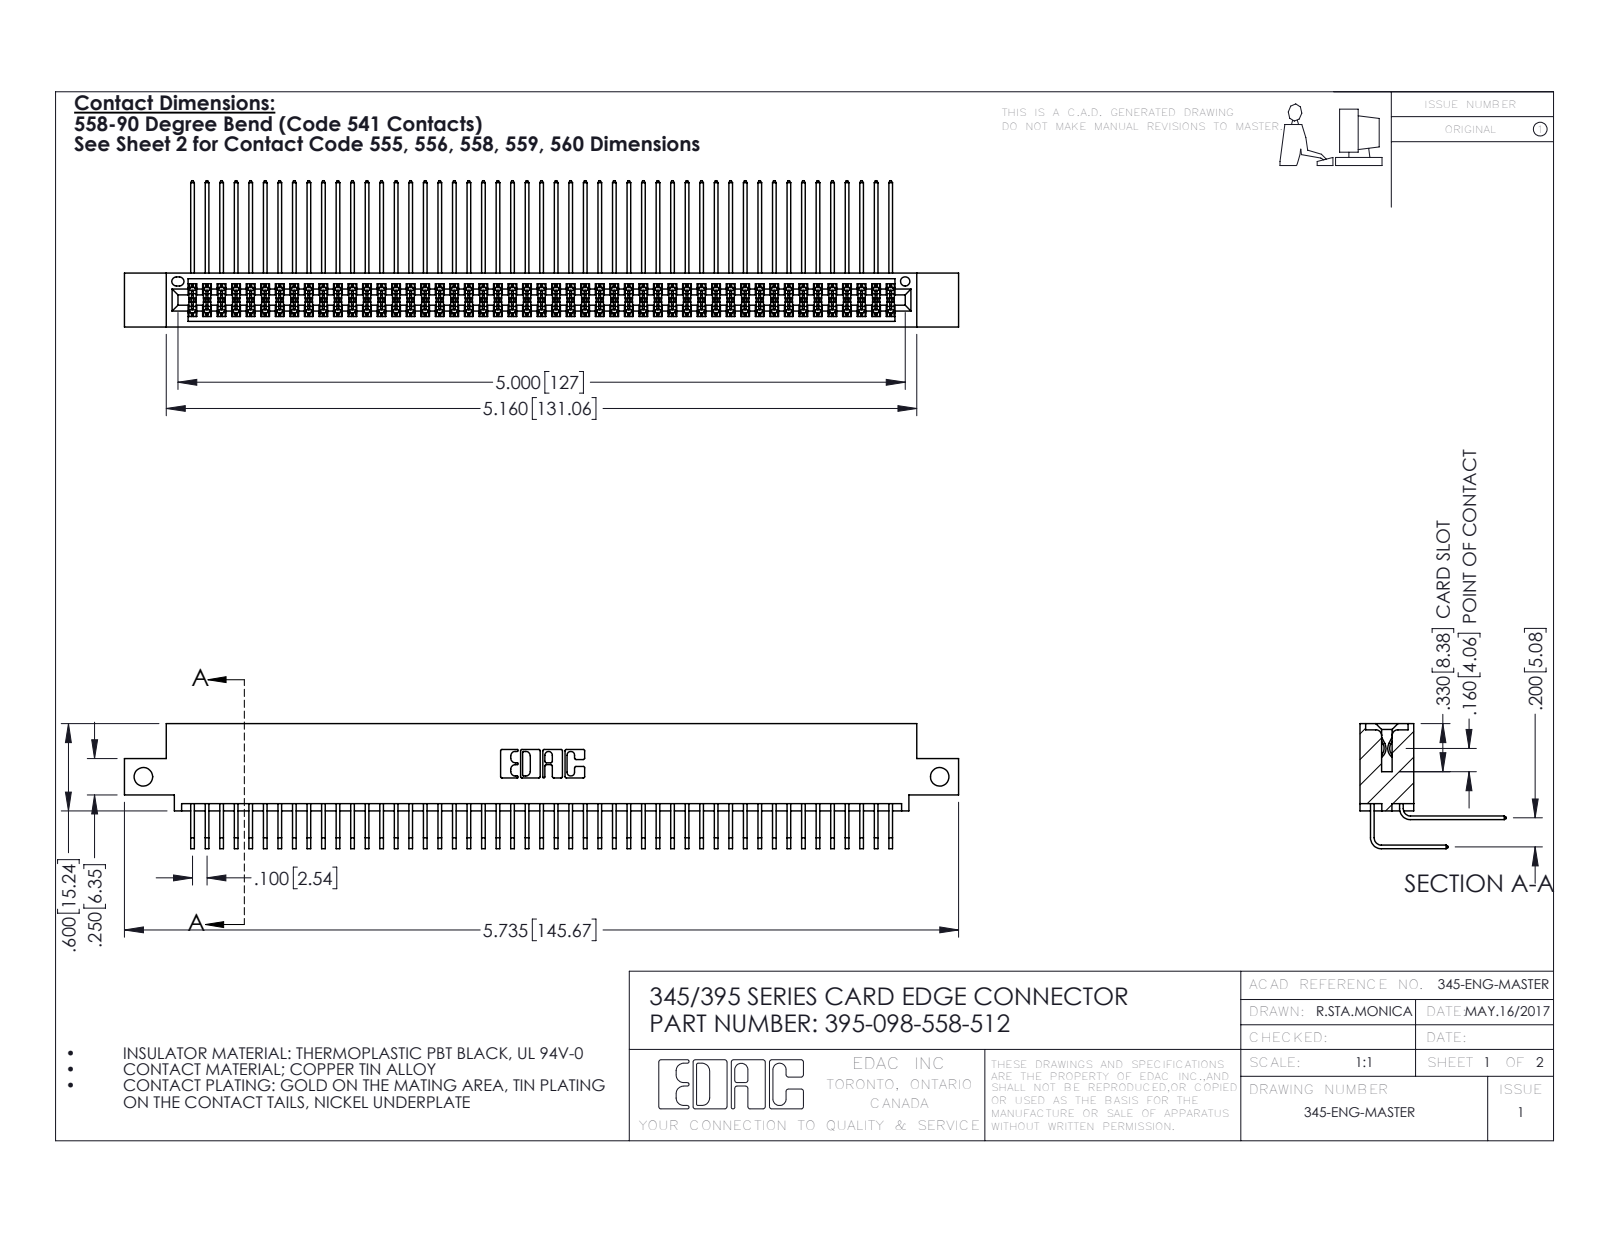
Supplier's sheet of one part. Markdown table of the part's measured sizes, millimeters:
| quantity | value |
| --- | --- |
| part name | 345 Part_0.110 Offset - Side Mount; 395-098-558-512; 345-292-001_558 Tail - 2; 345-292-001_558 559 Tail - 1 |
| STEP written by | SolidWorks 2016 (CONFIG_CONTROL_DESIGN) |
| units | millimeters |
| bodies | 99 solids, 5226 faces (3514 planar, 1712 cylindrical, 0 other) |
| overall size | 145.7 × 25.5 × 21.8 |
| volume | 14 600 mm³ |
| surface area | 24 360 mm² |
| round holes (diameter × count) | 3.3 × 2, 1.6 × 1 |
| partial cylindrical surfaces (radius × count) | 0.2 × 148, 0.3 × 22, 0.2 × 6, 0.8 × 6, 0.7 × 3, 0.4 × 2, 0.5 × 2, 0.6 × 2 |
| main face-to-face distances | 1.8, 7.6, 5.1, 9.4, 2.5, 6.9, 0.6, 5.7, 0.6, 4.4 |
| hole center spacings | 139.1 |
